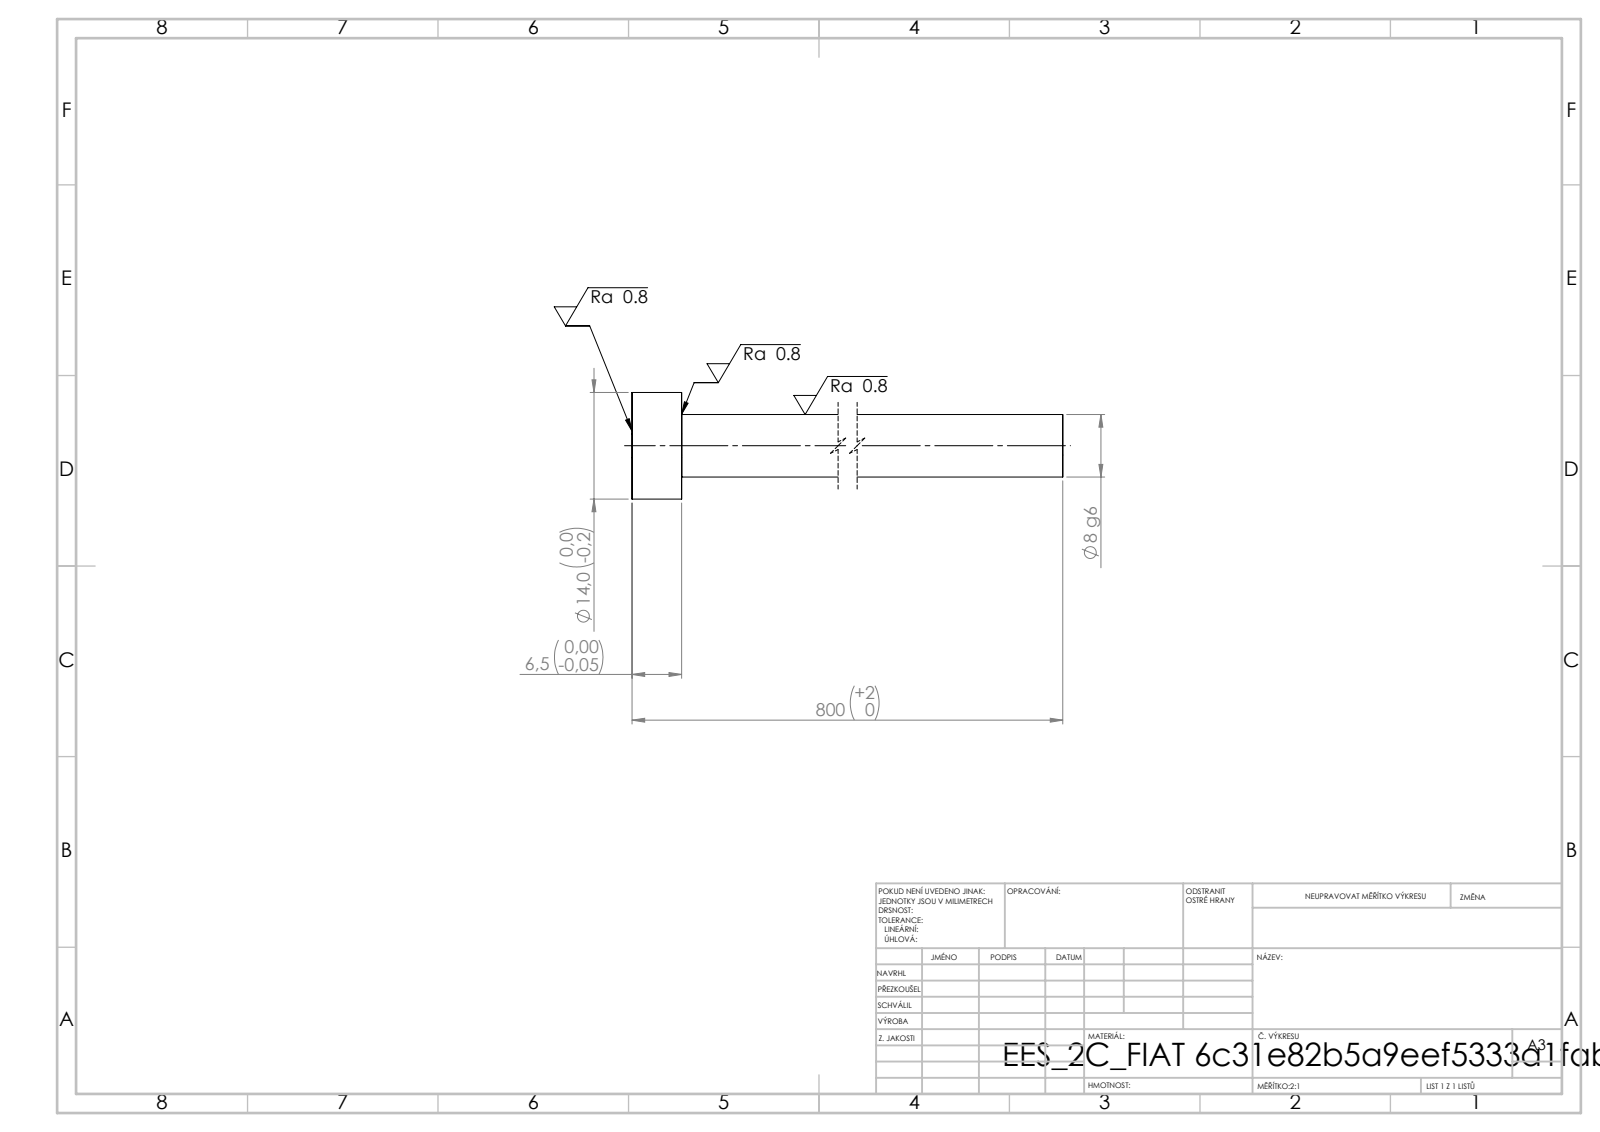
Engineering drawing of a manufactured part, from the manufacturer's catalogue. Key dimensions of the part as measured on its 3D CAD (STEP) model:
STEP written by: SolidWorks 2019 (CONFIG_CONTROL_DESIGN)
Units: millimetres
Bodies: 1 solid, 7 faces (3 planar, 4 cylindrical, 0 other)
Overall size (bounding box): 800 × 14 × 14
Volume: 42 905 mm³ · Surface area: 21 035 mm²
Round bosses / shafts (diameter × count): ⌀14 ×1, ⌀8.2 ×1
Main face-to-face distances: 6.5, 800, 793.5
